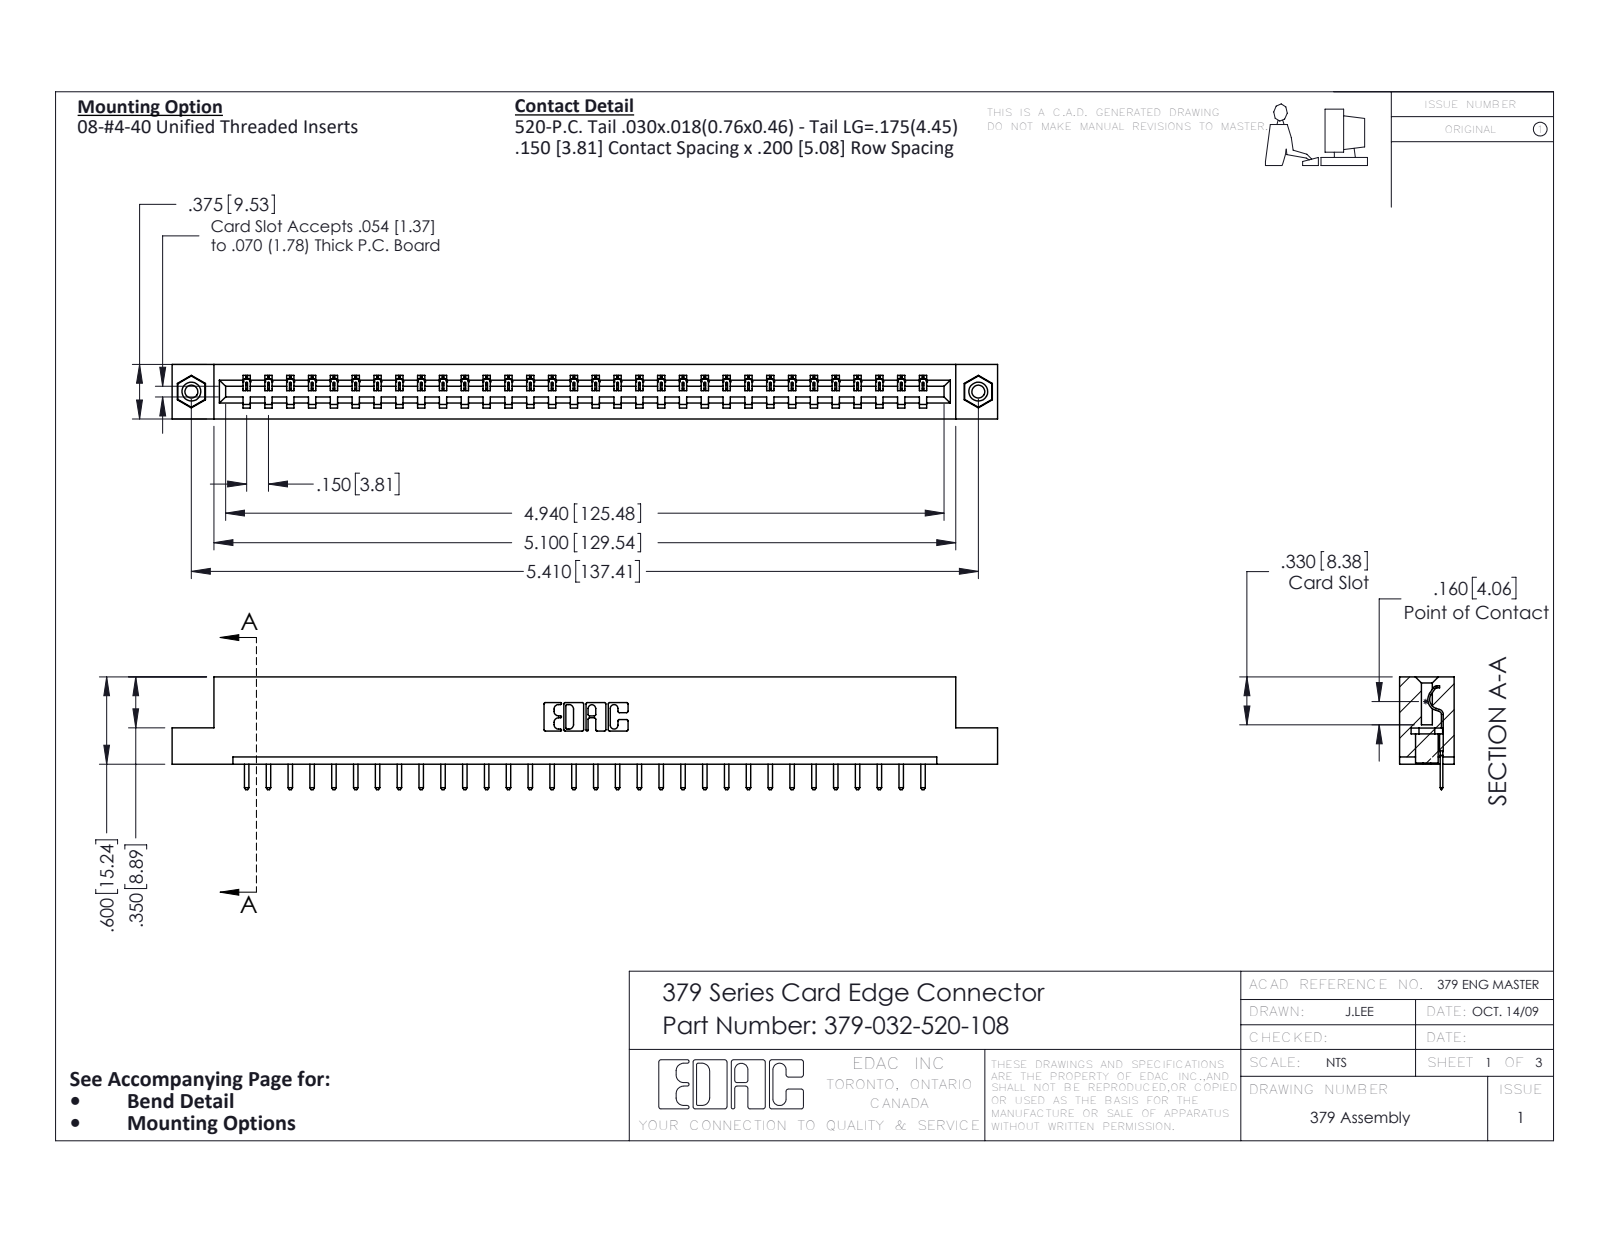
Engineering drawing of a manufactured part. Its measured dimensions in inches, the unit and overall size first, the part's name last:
Units: inches
Overall size (bounding box): 5.675 × 0.775 × 0.375
Round holes (diameter × count): ⌀0.089 ×2, ⌀0.125 ×2, ⌀0.156 ×2
Round bosses / shafts (diameter × count): ⌀0.155 ×2
Partial cylindrical surfaces — rounded edges, fillets, slot ends (radius × count): R0.01 ×66, R0.006 ×64, R0.01 ×22, R0.007 ×6, R0.031 ×6, R0.026 ×3, R0.014 ×1, R0.022 ×1
Main face-to-face distances: 0.3, 0.075, 0.375, 0.225, 0.6, 0.55, 0.2, 0.15, 0.15, 0.15
Hole centre spacings: 5.41
Volume: 0.911 in³ · Surface area: 23.13 in²
Bodies: 35 solids, 2158 faces (1510 planar, 632 cylindrical, 16 other)
Part name (STEP PRODUCT): 379 Part_Flush - .156 Dia - TI; 345-250-001_345-250-003-102; 379-032-520-108; 345-292-001_345-293-120
STEP written by: SolidWorks 2016 (CONFIG_CONTROL_DESIGN)
